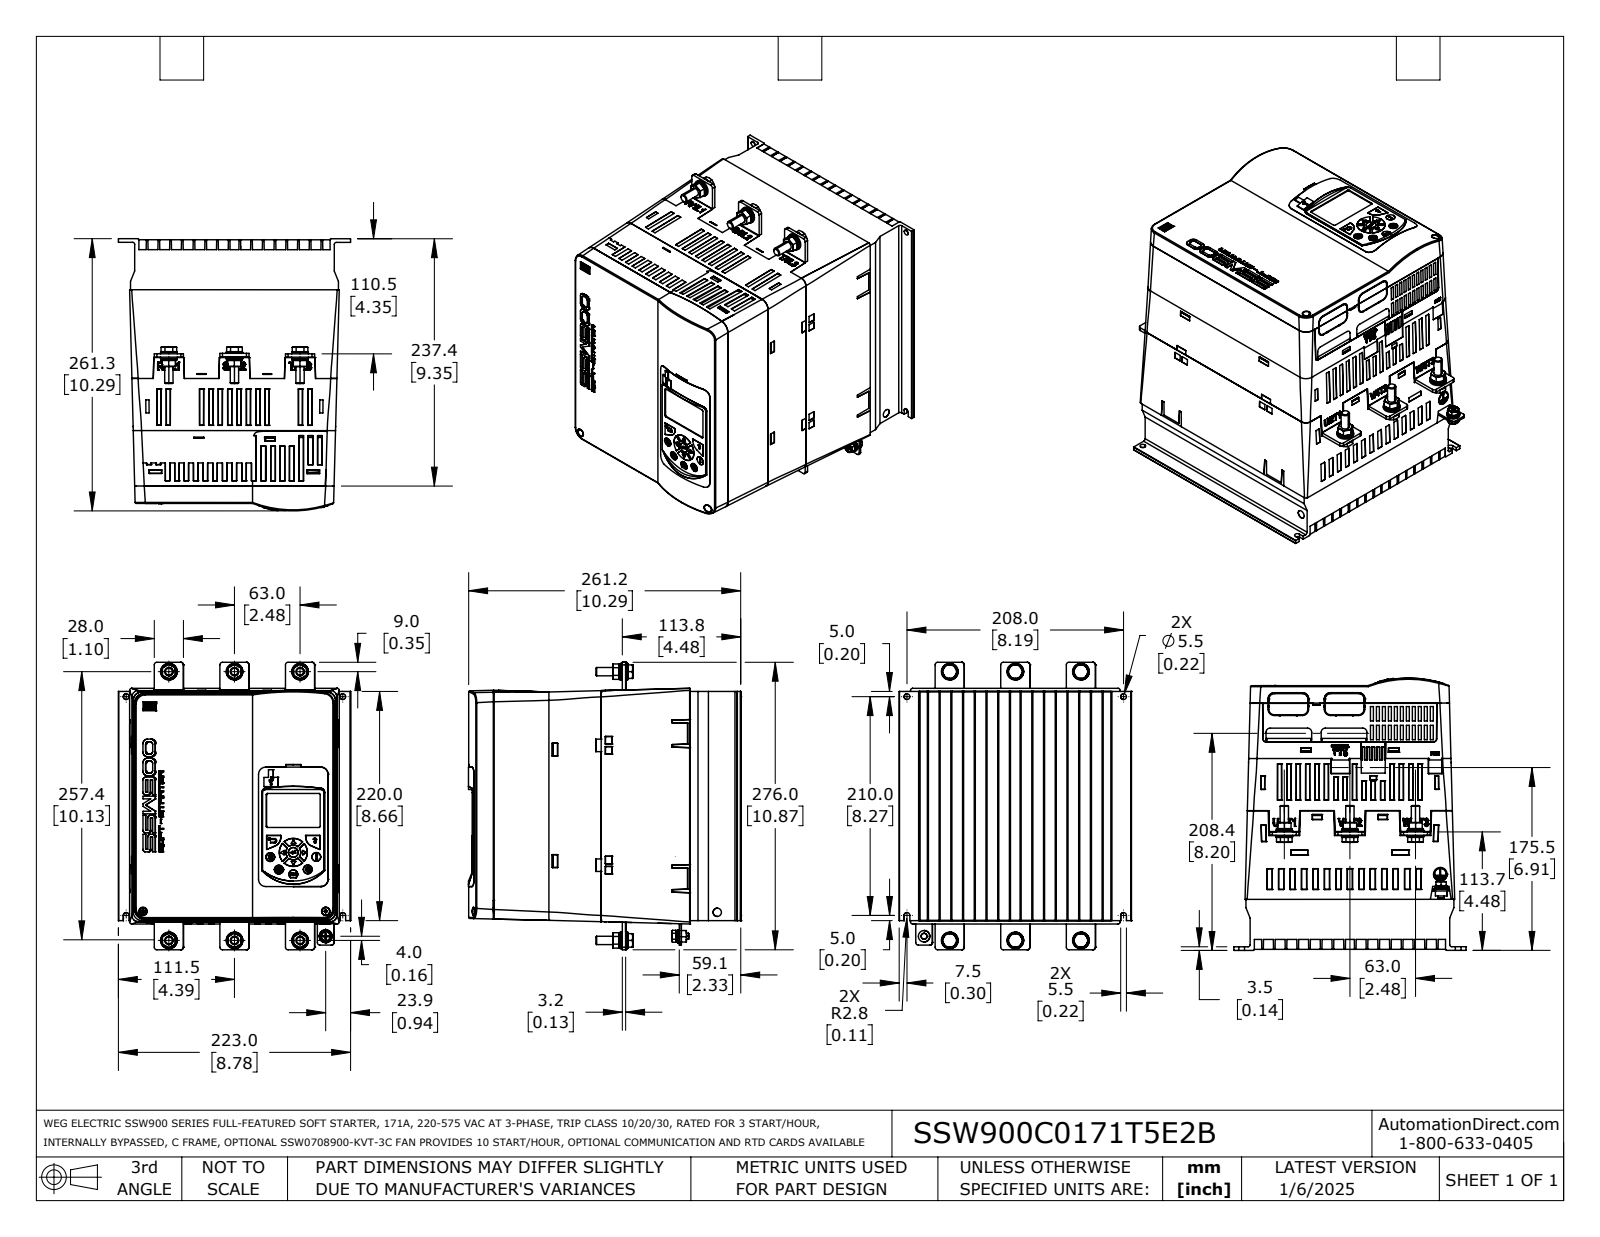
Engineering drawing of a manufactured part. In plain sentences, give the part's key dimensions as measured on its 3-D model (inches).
The part is named "SSW900C0171T5E2B". Its 3-D file was written by "SolidWorks 2021 (AUTOMOTIVE_DESIGN)". It is 11 solids with 4292 faces: 2981 planar, 513 cylindrical and 798 other. Overall it measures 10.866 by 10.296 by 8.78 inches. Its volume is 104.6 cubic inches and its surface area 1 019 square inches. Round holes: 6 of diameter 0.315, 2 of diameter 0.094, 2 of diameter 0.217, 1 of diameter 0.096, 1 of diameter 0.133, 1 of diameter 0.197, 1 of diameter 0.294, 1 of diameter 0.335, 1 of diameter 0.406, 1 of diameter 0.453. Round bosses or shafts: 6 of diameter 0.63, 6 of diameter 0.6, 4 of diameter 0.591, 2 of diameter 0.315, 1 of diameter 0.512, 1 of diameter 0.488, 1 of diameter 0.433, 1 of diameter 0.362. Partial cylindrical surfaces (rounded edges, fillets, slot ends): 121 of radius 0.012, 42 of radius 0.02, 16 of radius 0.008, 16 of radius 0.03, 14 of radius 0.098, 7 of radius 0.006, 6 of radius 0.024, 6 of radius 0.039. The main face-to-face distances are 7.302, 0.175, 0.102, 9.965, 9.79, 9.863, 9.688, 9.926, 9.751, 0.063. The hole center spacings are 0.941, 2.48, 8.139, 11.079, 0.981, 1.465, 1.466, 1.471.
